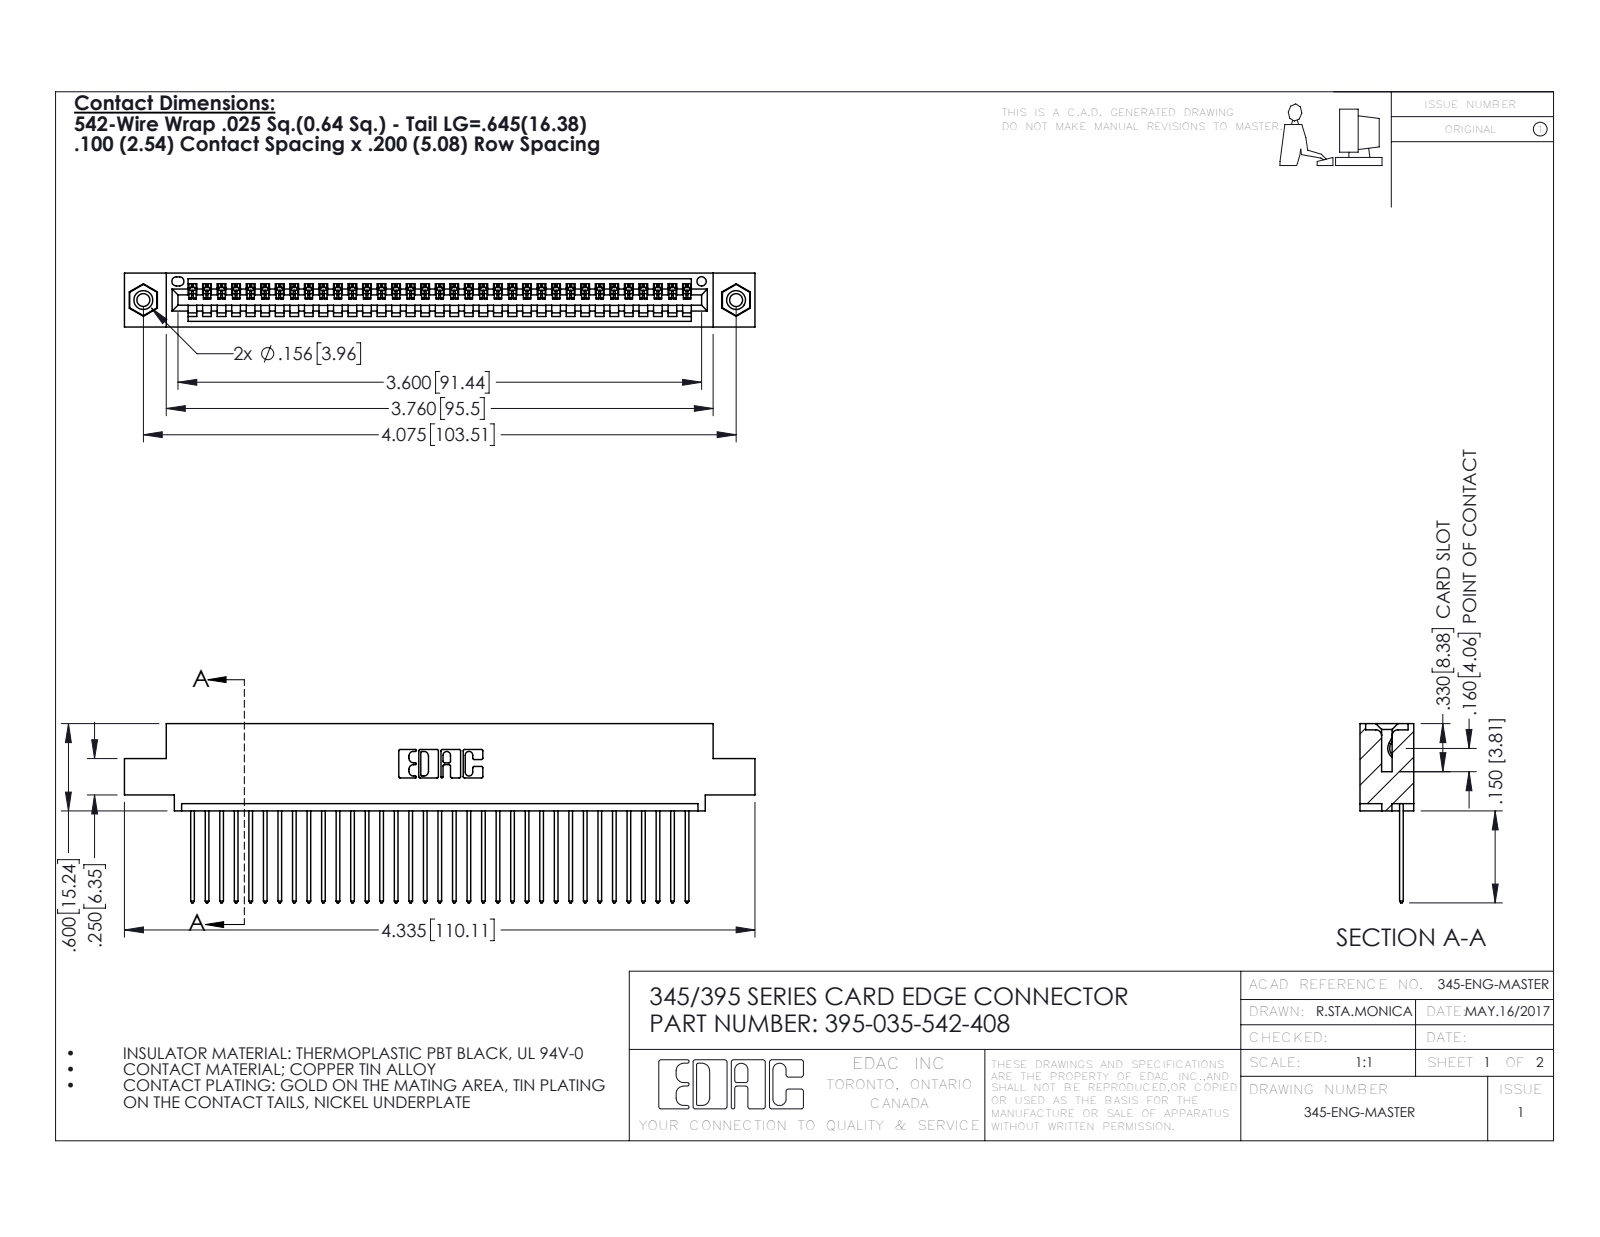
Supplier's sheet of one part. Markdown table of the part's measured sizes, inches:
| quantity | value |
| --- | --- |
| part name | 345-292-001_345-293-142; 345 Part_0.110 Offset - 0.156 Dia-TI; 345-250-001_345-250-003-102; 395-035-542-408 |
| STEP written by | SolidWorks 2016 (CONFIG_CONTROL_DESIGN) |
| units | inches |
| bodies | 38 solids, 2220 faces (1516 planar, 688 cylindrical, 16 other) |
| overall size | 4.335 × 1.232 × 0.37 |
| volume | 0.635 in³ |
| surface area | 22.19 in² |
| round holes (diameter × count) | 0.089 × 2, 0.125 × 2, 0.156 × 2, 0.064 × 1 |
| round bosses / shafts (diameter × count) | 0.155 × 2 |
| partial cylindrical surfaces (radius × count) | 0.006 × 70, 0.01 × 70, 0.01 × 22, 0.007 × 6, 0.031 × 6, 0.026 × 3, 0.031 × 2, 0.04 × 2 |
| main face-to-face distances | 0.072, 0.298, 0.37, 0.098, 0.272, 0.025, 0.2, 0.225, 0.149, 0.072 |
| hole center spacings | 0.27, 3.839, 4.075 |
